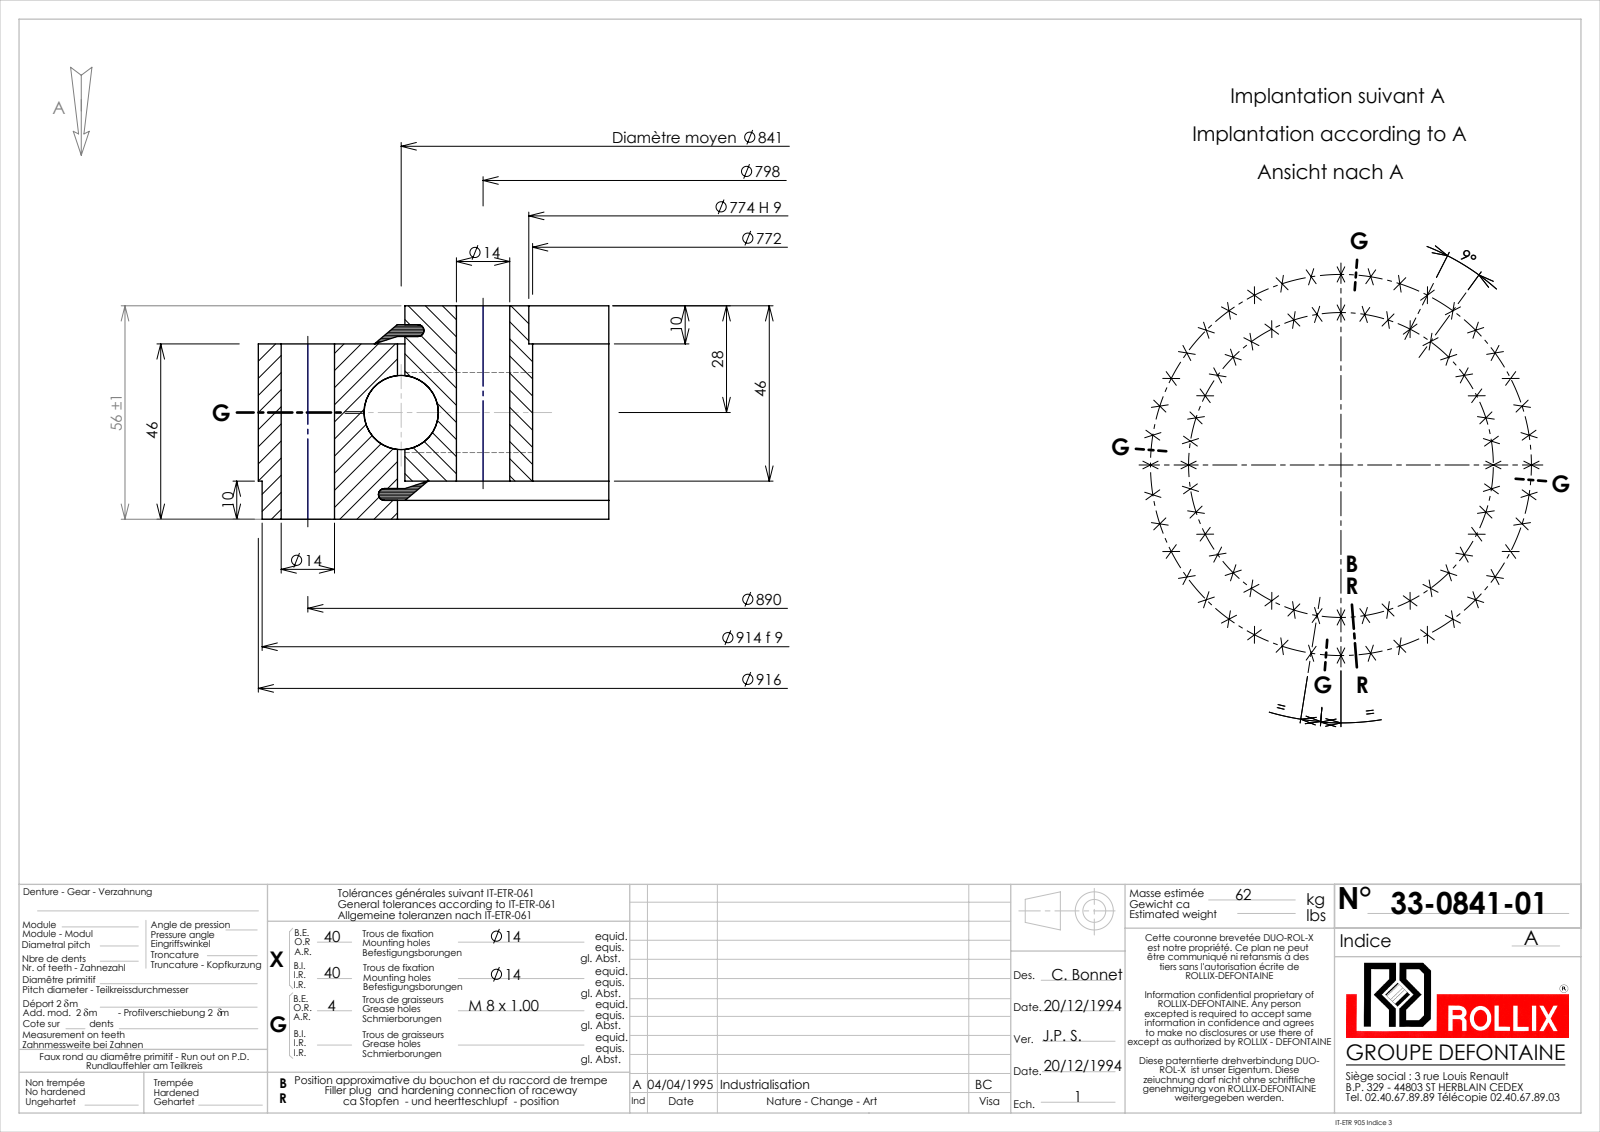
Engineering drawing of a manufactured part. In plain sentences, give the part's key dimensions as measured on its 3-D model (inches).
The part is named "33-0841-01". Its 3-D file was written by "SolidWorks 2016 (CONFIG_CONTROL_DESIGN)". It is 9 solids with 318 faces: 54 planar, 196 cylindrical and 68 other. Overall it measures 36.722 by 36.722 by 2.205 inches. Its volume is 446.8 cubic inches and its surface area 1 944 square inches. Round holes: 80 of diameter 0.551, 4 of diameter 0.276, 1 of diameter 30.394, 1 of diameter 30.472, 1 of diameter 33.187. Round bosses or shafts: 4 of diameter 0.315, 1 of diameter 36.063, 1 of diameter 35.984, 1 of diameter 33.033. The main face-to-face distances are 1.811, 0.394, 1.417, 2.205, 0.195, 2.01, 0.199, 1.616, 0.317, 1.888. The hole center spacings are 2.465, 7.334, 12.023, 9.709, 20.404, 14.263, 23.89, 25.417.
